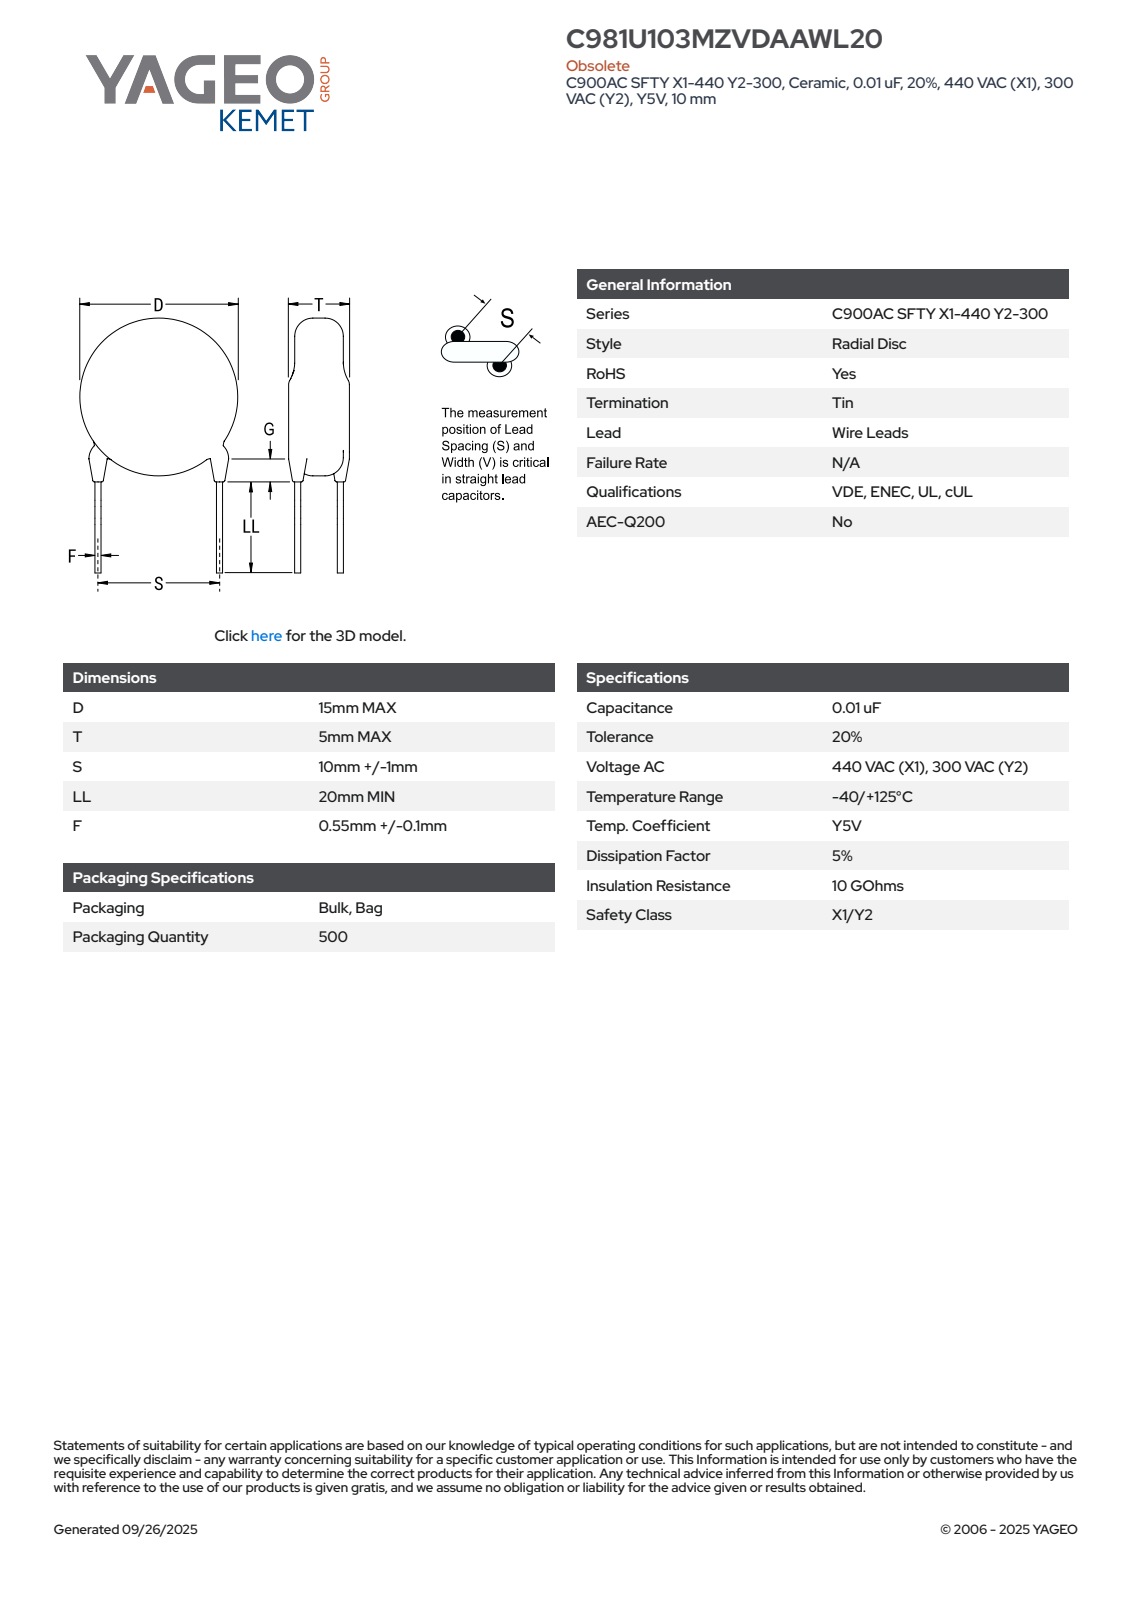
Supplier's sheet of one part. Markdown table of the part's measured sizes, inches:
| quantity | value |
| --- | --- |
| part name | CCD_STC900_D15T5S10LL20F0.65G3 |
| STEP written by | SolidWorks 2014 (AUTOMOTIVE_DESIGN) |
| units | inches |
| bodies | 4 solids, 83 faces (61 planar, 6 cylindrical, 16 other) |
| overall size | 1.389 × 0.591 × 0.197 |
| volume | 0.054 in³ |
| surface area | 1.02 in² |
| round bosses / shafts (diameter × count) | 0.026 × 2, 0.591 × 1 |
| main face-to-face distances | 0.197, 1.128, 1.059, 0.068, 0.013, 0.055, 0.013, 0.202, 0.21, 1.072 |
